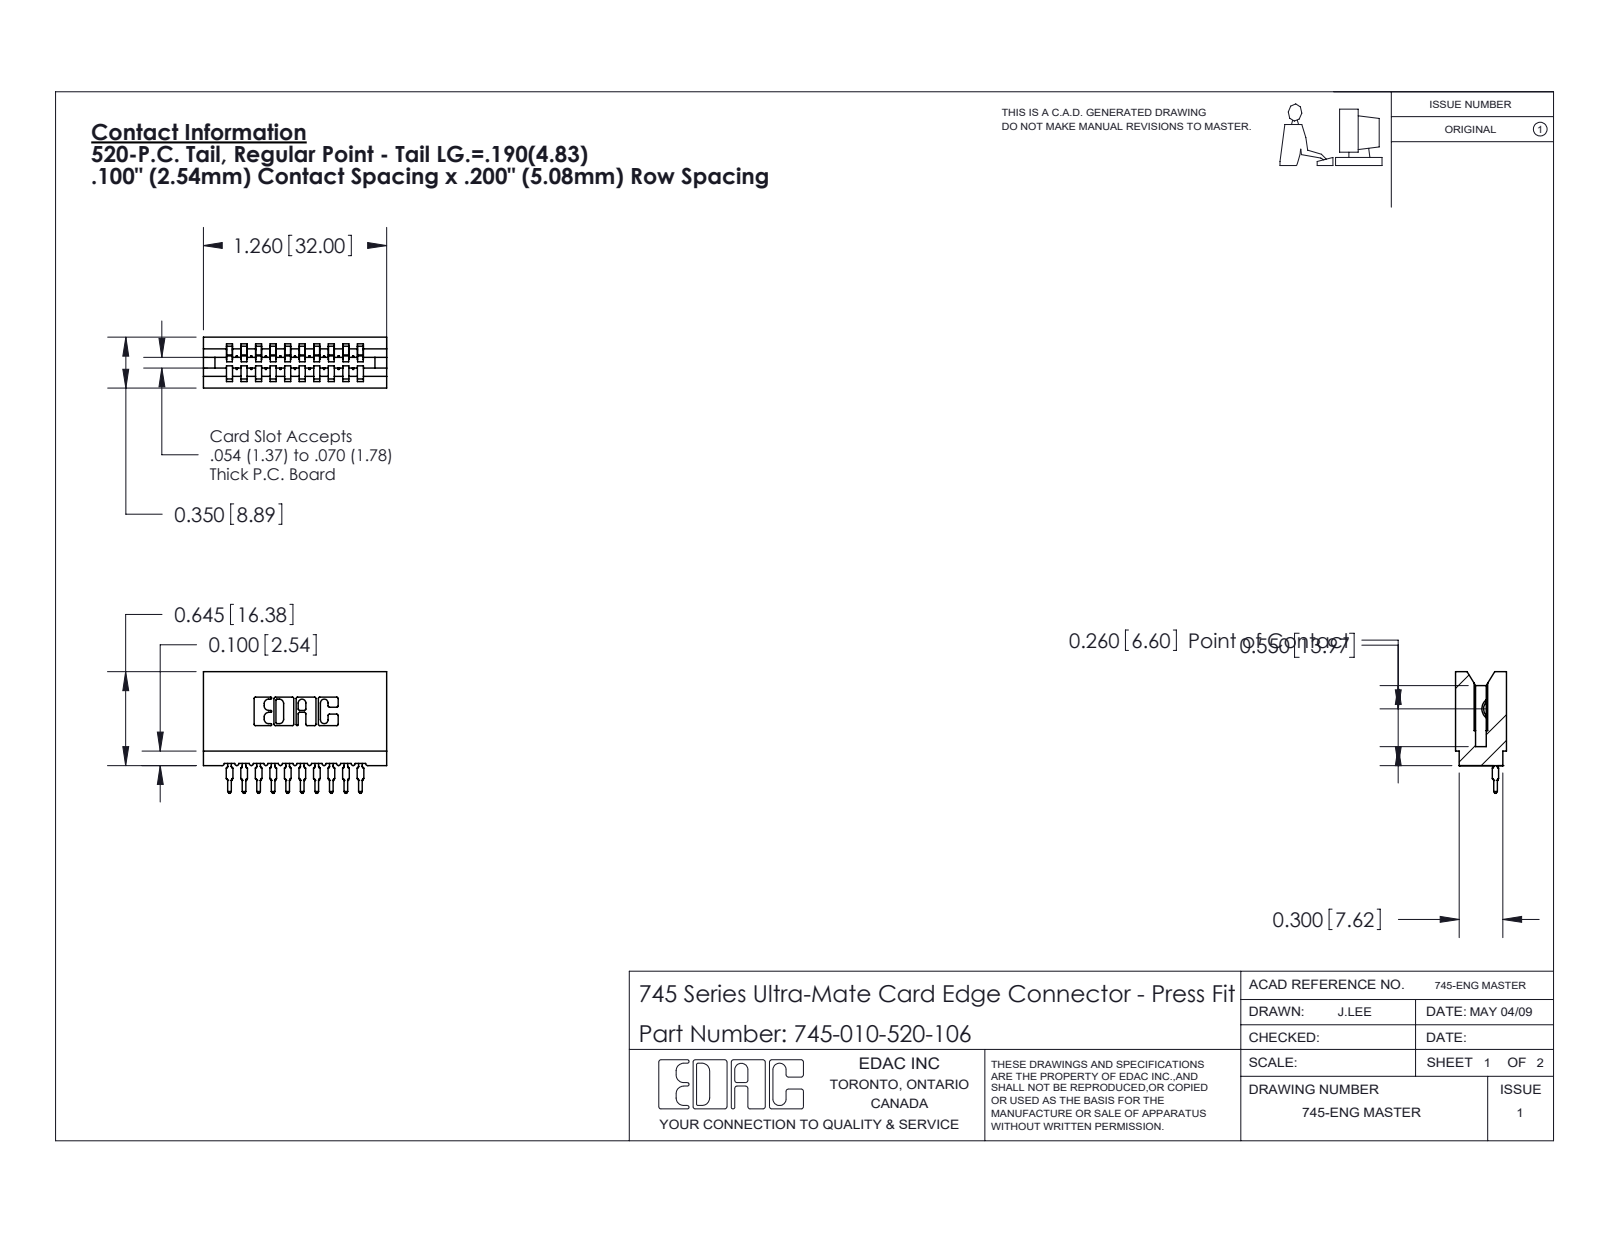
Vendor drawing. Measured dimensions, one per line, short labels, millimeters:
name: 745-010-520-106; 745-292-001_520; 745 Part_Insulator Option - 06
written by: SolidWorks 2020 (CONFIG_CONTROL_DESIGN)
unit: mm
bodies: 11 solids, 1216 faces (726 planar, 230 cylindrical, 260 other)
size: 32 × 21.2 × 8.9
volume: 2 950 mm³; area: 4 825 mm²
rounds: 22× R0.3, 20× R0.4, 20× R0.5, 6× R0.2, 6× R0.8, 4× R0.1, 4× R0.3, 3× R0.7
face distances: 2.5, 5.1, 7.6, 10.2, 1.1, 3.6, 12.7, 1.5, 6.1, 4
